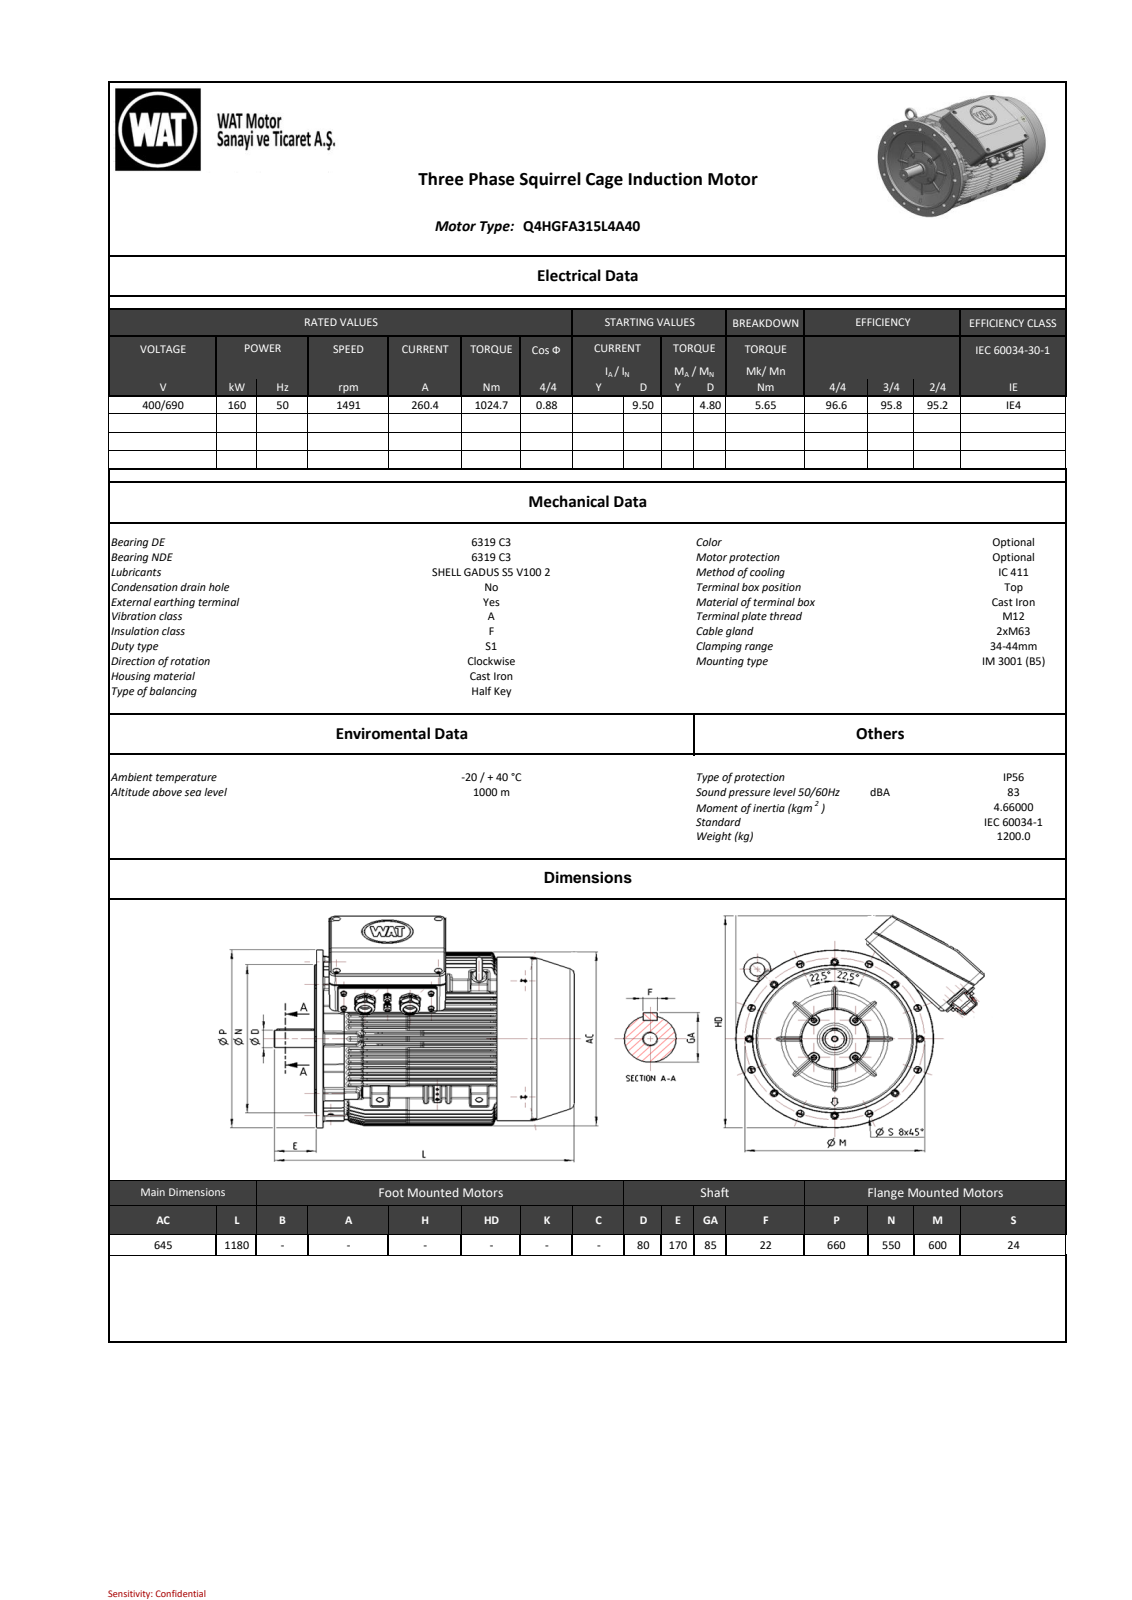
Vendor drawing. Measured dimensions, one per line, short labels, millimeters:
name: 26009910674F4pu1
written by: SIEMENS PLM Software NX 11.0 (AUTOMOTIVE_DESIGN)
unit: mm
bodies: 0 solids, 5751 faces (2602 planar, 1193 cylindrical, 1956 other)
size: 1180 × 829.19 × 785.69
holes: 8× ⌀24, 8× ⌀26, 7× ⌀20, 5× ⌀8.5, 4× ⌀9, 4× ⌀22, 2× ⌀5.3, 2× ⌀8, 2× ⌀12, 2× ⌀15, 2× ⌀21, 2× ⌀44
bosses: 8× ⌀16, 6× ⌀20, 4× ⌀10, 2× ⌀64.8, 2× ⌀50, 1× ⌀660, 1× ⌀607, 1× ⌀565
rounds: 463× R6, 161× R3, 66× R2.09, 61× R2.61, 35× R0.8, 26× R10, 24× R1.5, 15× R0.4
face distances: 117, 20.71, 305.15, 41.51, 284.35, 20.8, 263.64, 242.48, 83.38, 62.4
hole spacings: 486.48, 115.07, 115.08, 218.13, 300, 325.24, 325.26, 424.26
